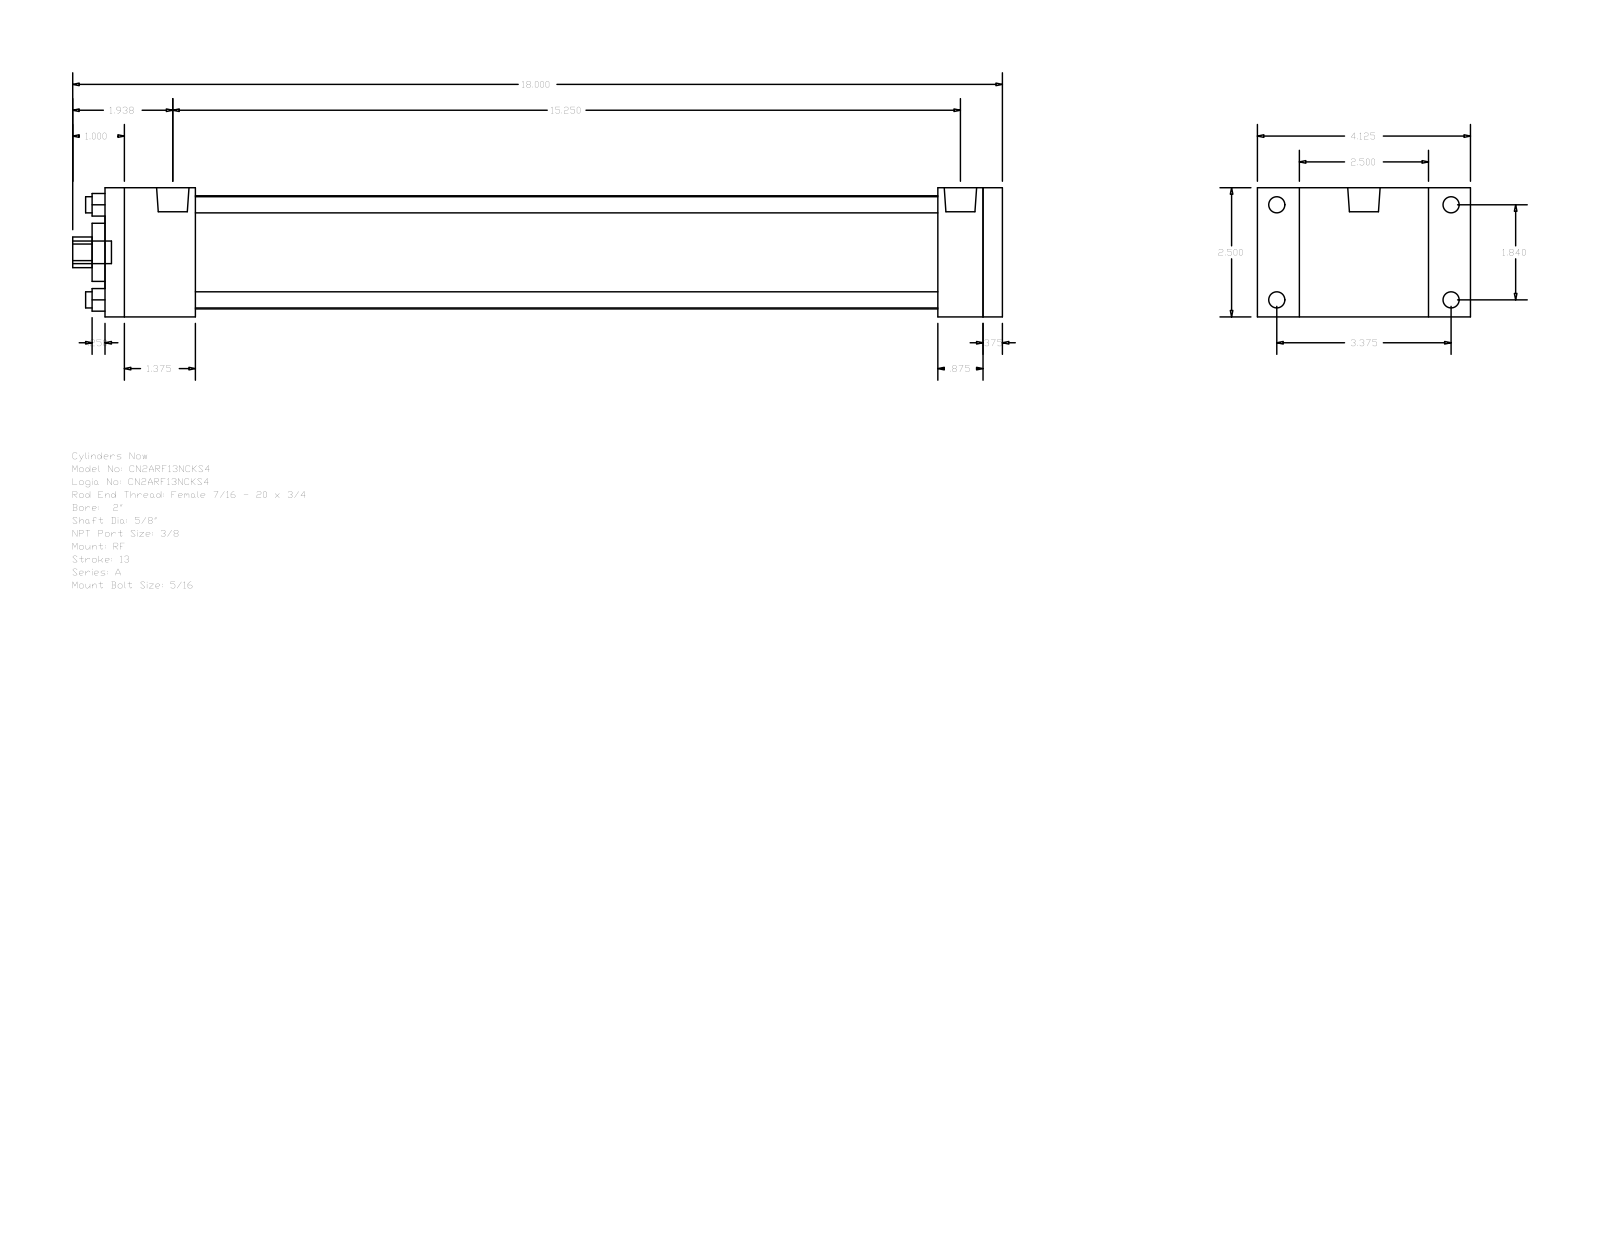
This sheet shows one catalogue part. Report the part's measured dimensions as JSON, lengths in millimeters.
{"part_name": "A_RF__0200_0.625", "step_written_by": "GSSL Pune (CONFIG_CONTROL_DESIGN)", "units": "millimeters", "bodies": {"solids": 0, "faces": 92, "planar": 64, "cylindrical": 28, "other": 0}, "overall_size": [457.2, 104.78, 63.5], "round_holes": [[7.94, 4], [15.88, 1], [28.57, 1], [55.63, 1]], "round_bosses_or_shafts": [[7.94, 4], [5.56, 4], [15.93, 2], [11.11, 1]], "partial_cylinders_radius": [[7.54, 1]], "face_to_face_distances": [63.5, 441.32, 9.52, 431.8, 44.45, 387.35, 396.87, 409.57, 365.12, 22.23], "hole_center_spacings": [33.05, 46.74, 66.1]}
